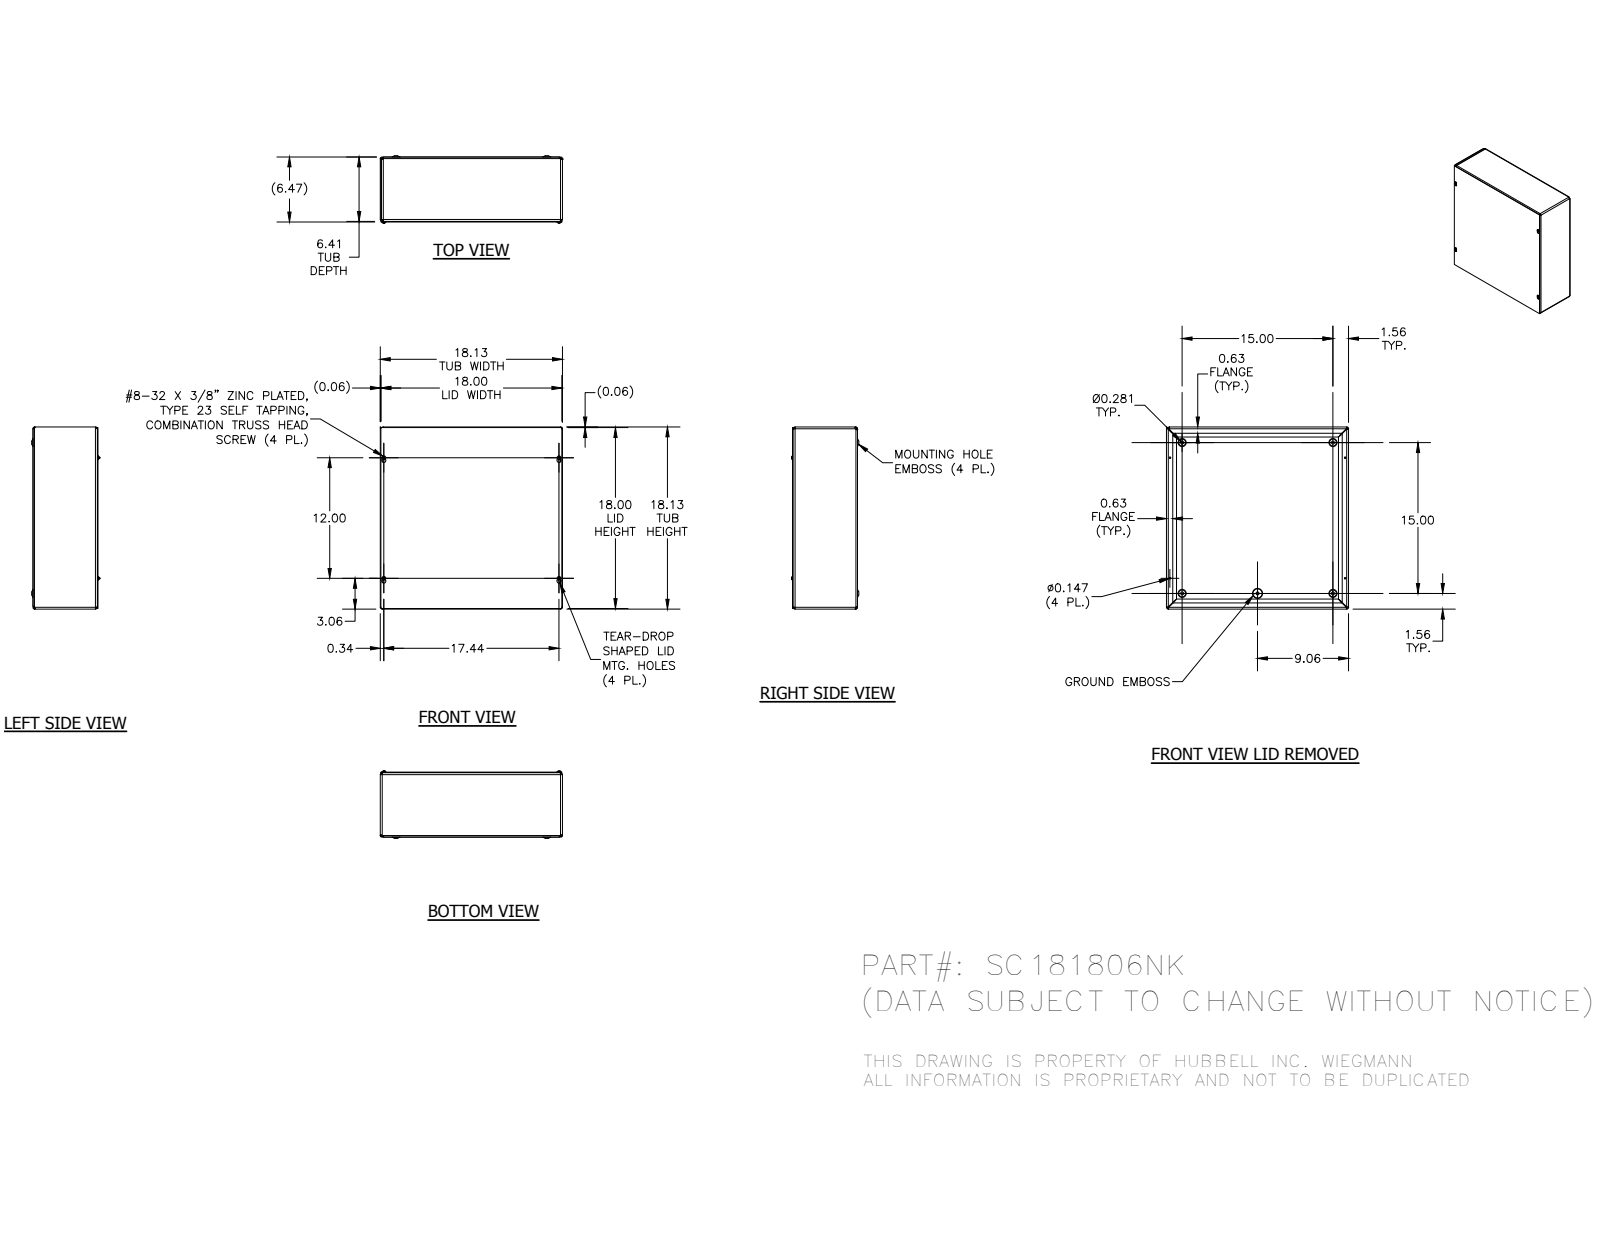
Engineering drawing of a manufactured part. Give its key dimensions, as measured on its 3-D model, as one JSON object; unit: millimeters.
{"part_name": "SC1818BKP; SC181806NKWRA; SC1818LID; 34056 (+1 more)", "step_written_by": "Autodesk Inventor 2014 (AUTOMOTIVE_DESIGN)", "units": "millimeters", "bodies": {"solids": 7, "faces": 357, "planar": 132, "cylindrical": 67, "other": 158}, "overall_size": [460.38, 460.38, 170], "volume_mm3": 1216000, "surface_area_mm2": 1555000, "round_holes": [[3.73, 4], [7.62, 4], [4.19, 1]], "round_bosses_or_shafts": [[9.75, 4], [4.17, 4], [5.8, 1]], "partial_cylinders_radius": [[3.17, 12], [4.75, 8], [1.4, 4], [1.57, 4], [2.38, 4], [2.97, 4], [3.15, 4], [3.96, 4]], "face_to_face_distances": [1.57, 161.12, 162.69, 1.59, 162.71, 164.28, 1.58, 458.8, 457.23, 460.38], "hole_center_spacings": [49.09, 344.29, 381, 190.5, 304.8, 413.71, 413.72, 425.97]}
